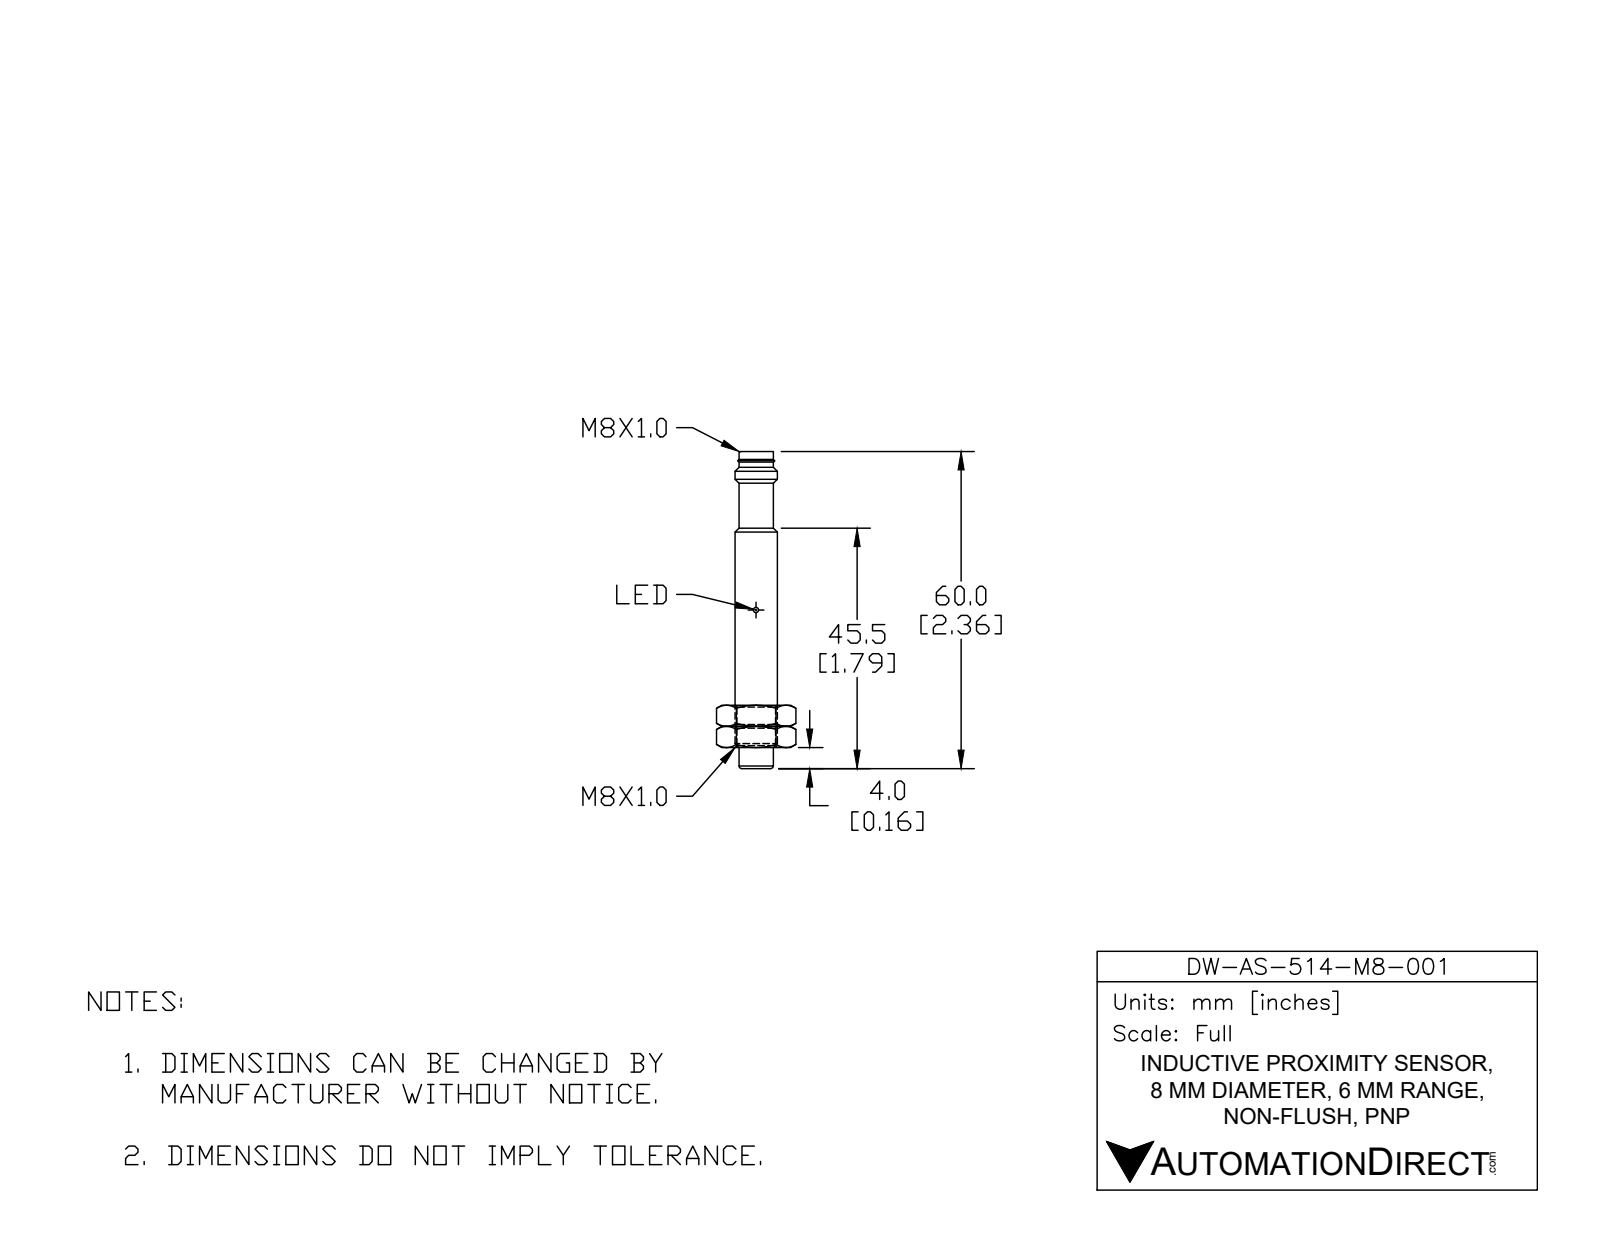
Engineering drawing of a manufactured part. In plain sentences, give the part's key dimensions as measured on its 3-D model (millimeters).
The part is named "DW-AS-514-M8-001". Its 3-D file was written by "SolidWorks 2017 (AUTOMOTIVE_DESIGN)". It is 1 solid with 33 faces: 3 planar, 18 cylindrical and 12 other. Overall it measures 60 by 8 by 8 millimeters. Its volume is 2 620 cubic millimeters and its surface area 1 681 square millimeters. Round holes: 2 of diameter 1.8. Round bosses or shafts: 3 of diameter 1, 1 of diameter 8, 1 of diameter 6.9, 1 of diameter 6.5, 1 of diameter 6. The main face-to-face distances are 55, 60, 5.
